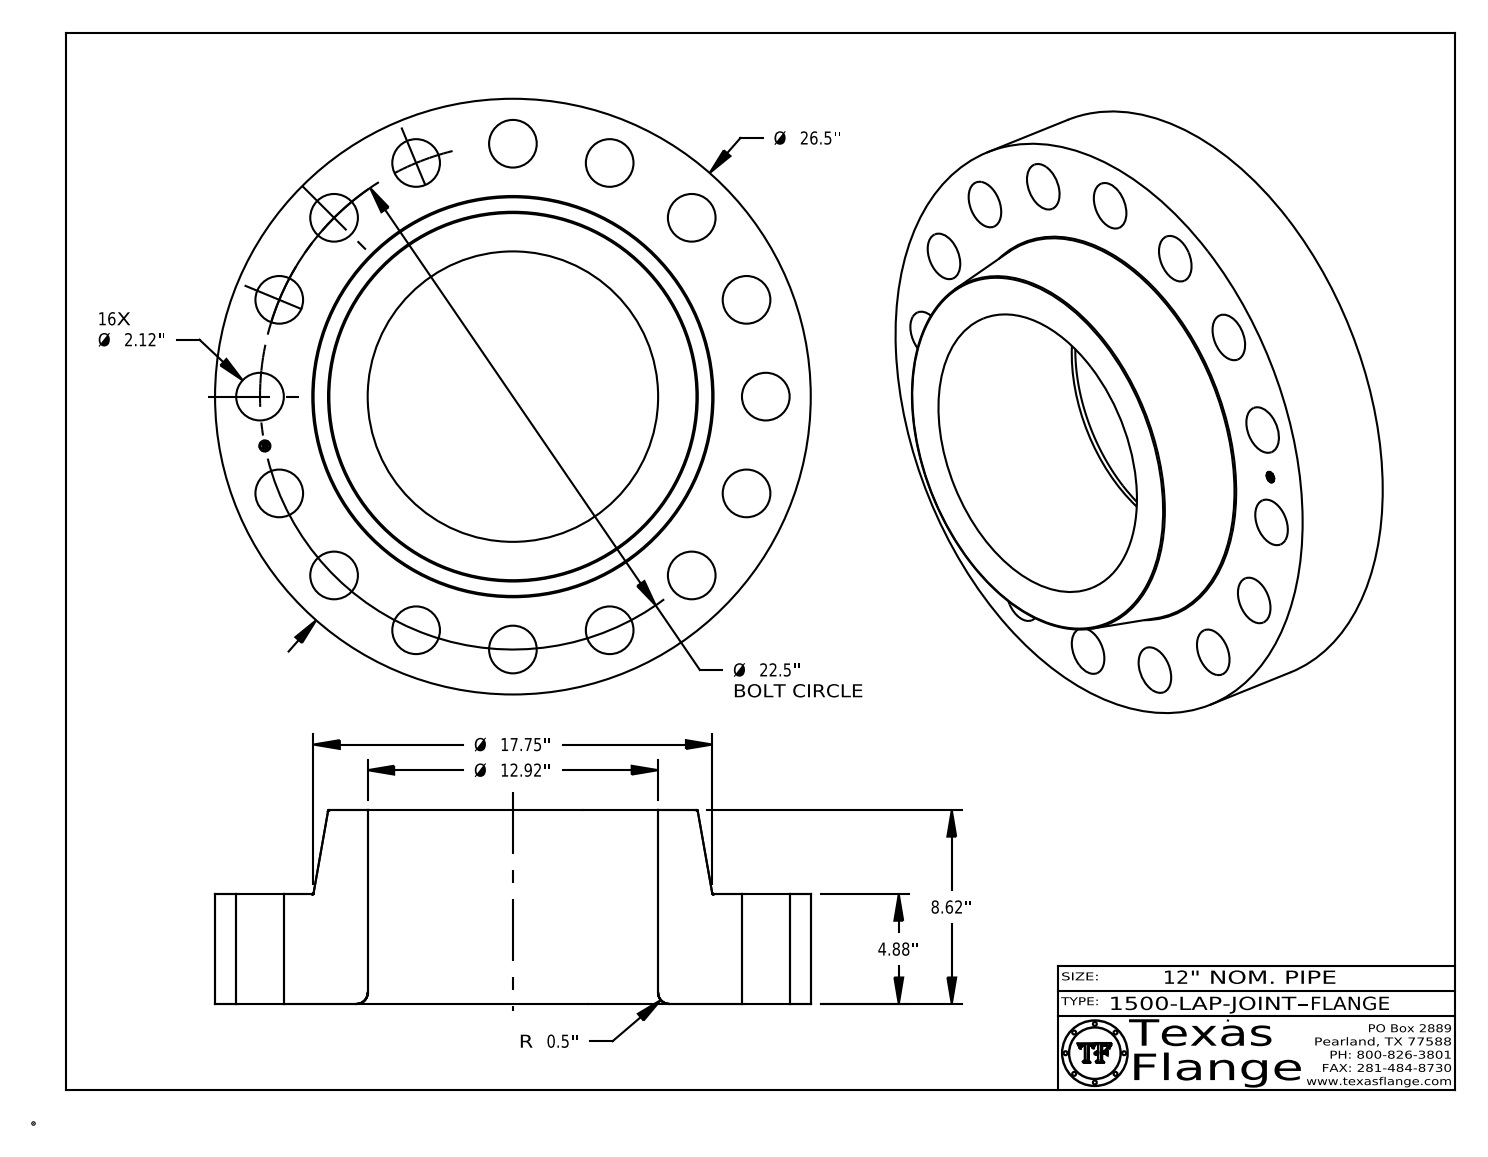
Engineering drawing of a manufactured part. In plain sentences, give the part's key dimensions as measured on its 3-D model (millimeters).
The part is named "1500-LAP-JOINT FLANGE". Its 3-D file was written by "CATIA V5 STEP AP214 (AUTOMOTIVE_DESIGN)". It is 1 solid with 432 faces: 368 planar, 56 cylindrical and 8 other. Overall it measures 673.1 by 673.1 by 218.9 millimeters. Its volume is 35 100 000 cubic millimeters and its surface area 1 395 000 square millimeters. Round holes: 16 of diameter 53.8, 1 of diameter 12.6, 1 of diameter 328.2. Round bosses or shafts: 8 of diameter 0.8, 1 of diameter 673.1, 1 of diameter 9.9. The main face-to-face distances are 124, 218.9, 95, 123.6, 0.4, 95.4, 3.8, 3.7, 0.7, 2.4. The hole center spacings are 317.5, 528, 560.5, 285.8, 218.7, 404.1, 111.5, 111.5.
